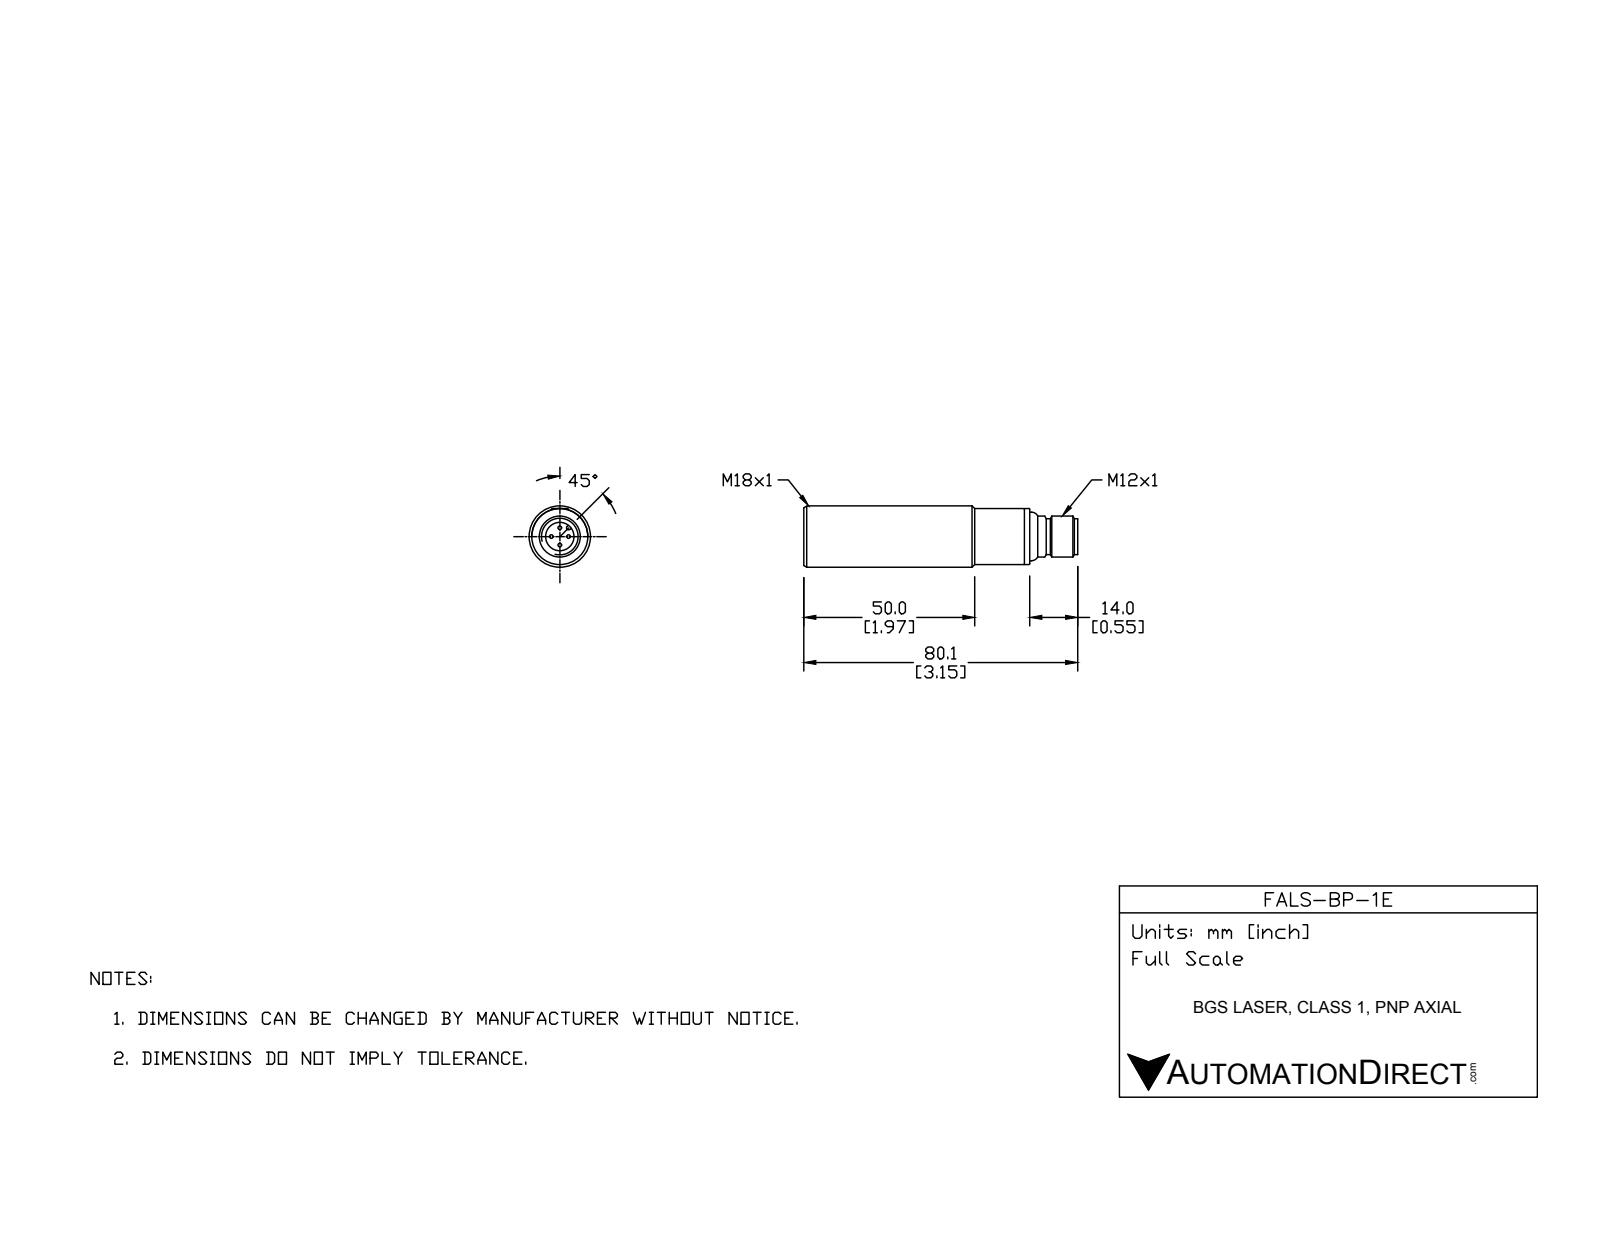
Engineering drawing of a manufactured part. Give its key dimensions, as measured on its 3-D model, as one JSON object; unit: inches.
{"part_name": "FALS-BP-1E", "step_written_by": "SolidWorks 2017 (AUTOMOTIVE_DESIGN)", "units": "inches", "bodies": {"solids": 10, "faces": 166, "planar": 50, "cylindrical": 73, "other": 43}, "overall_size": [3.154, 0.709, 0.709], "volume_in3": 1.039, "surface_area_in2": 10.09, "round_holes": [[0.039, 4], [0.043, 4], [0.106, 1], [0.185, 1], [0.278, 1], [0.327, 1], [0.622, 1]], "round_bosses_or_shafts": [[0.709, 1], [0.646, 1], [0.559, 1], [0.472, 1], [0.413, 1], [0.276, 1], [0.189, 1]], "partial_cylinders_radius": [[0.02, 4], [0.024, 1], [0.331, 1]], "face_to_face_distances": [0.063, 2.531, 0.055, 2.476, 2.469, 2.539, 2.594, 2.795, 2.74, 2.732], "hole_center_spacings": [0.098, 0.139, 0.197]}
